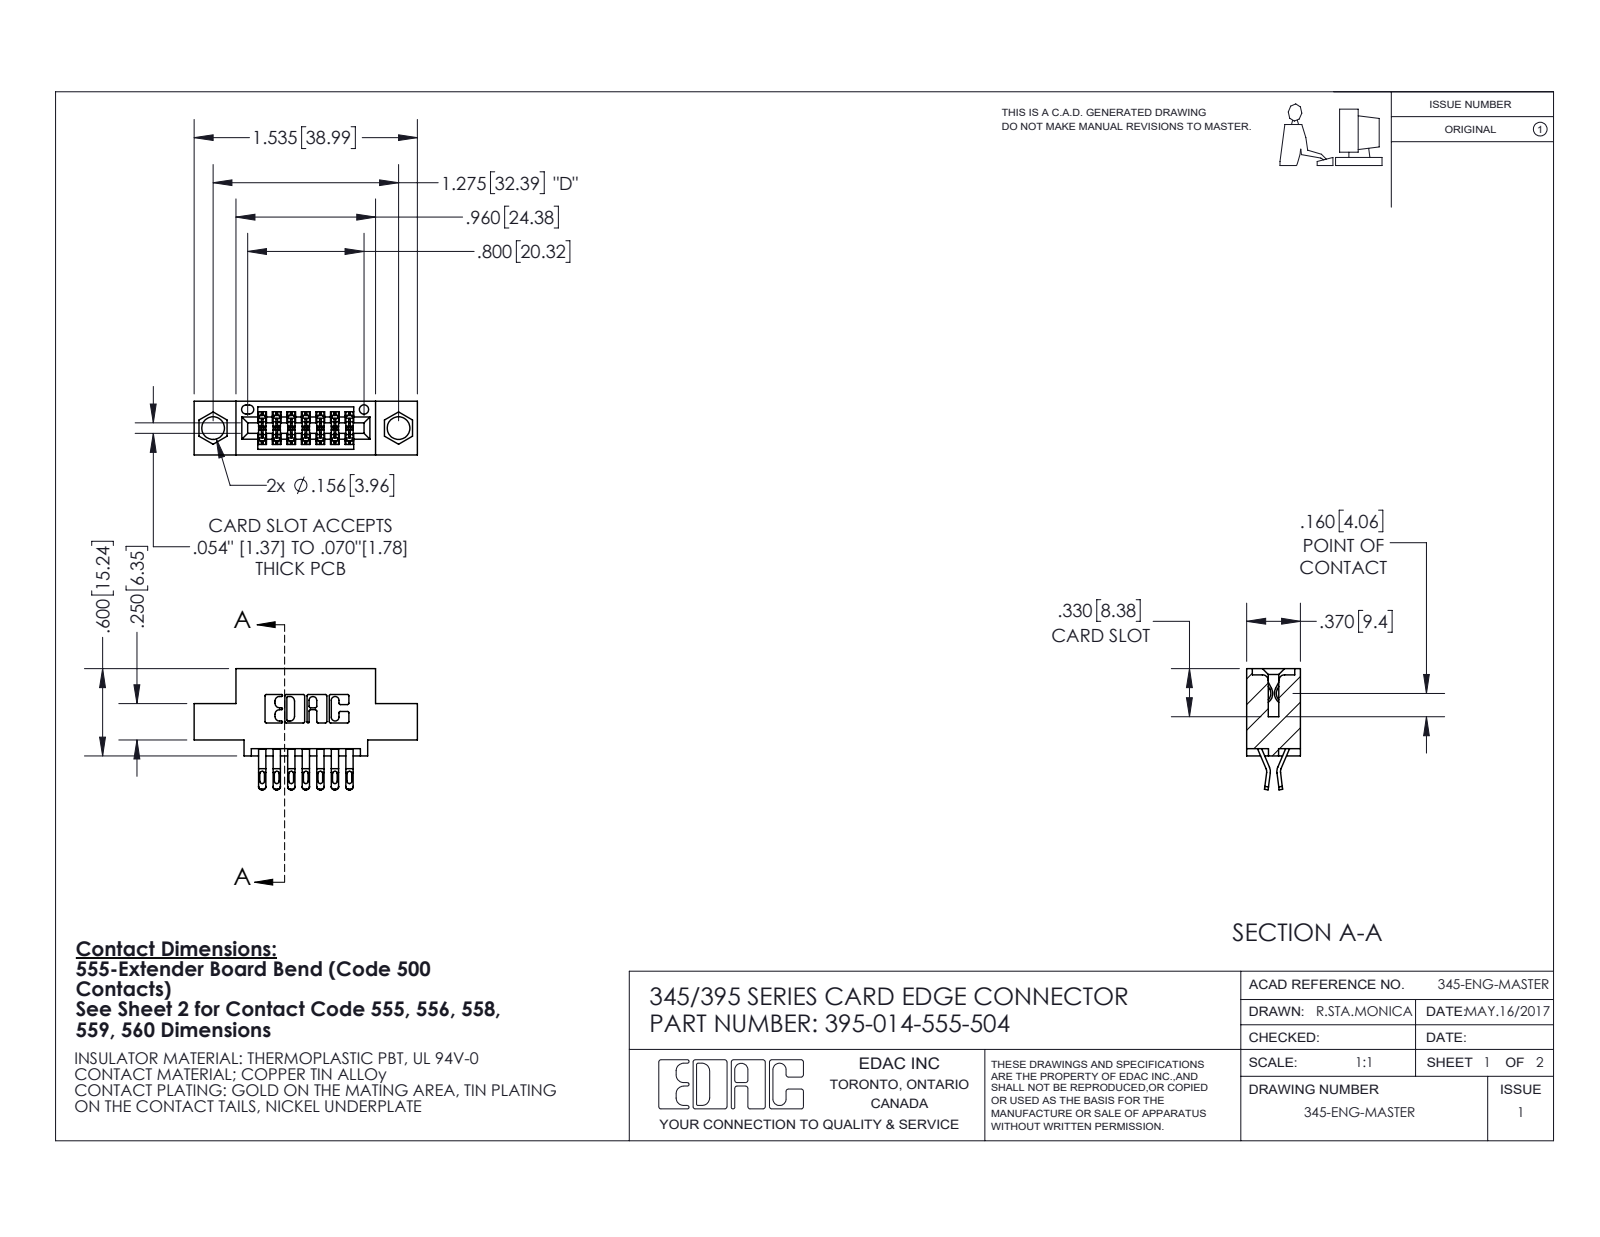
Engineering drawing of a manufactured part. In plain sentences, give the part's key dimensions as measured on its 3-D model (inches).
The part is named "345-292-001_555 Tail; 395-014-555-504; 345 Part_0.110 Offset - 0.156 Dia-TI". Its 3-D file was written by "SolidWorks 2020 (CONFIG_CONTROL_DESIGN)". It is 15 solids with 928 faces: 532 planar, 396 cylindrical and 0 other. Overall it measures 1.535 by 0.832 by 0.37 inches. Its volume is 0.203 cubic inches and its surface area 6.698 square inches. Round holes: 2 of diameter 0.156, 1 of diameter 0.064. Partial cylindrical surfaces (rounded edges, fillets, slot ends): 35 of radius 0.016, 28 of radius 0.006, 28 of radius 0.02, 22 of radius 0.01, 6 of radius 0.007, 6 of radius 0.031, 3 of radius 0.026, 2 of radius 0.01. The main face-to-face distances are 0.2, 0.298, 0.072, 0.37, 0.1, 0.025, 0.3, 0.098, 0.272, 0.16. The hole center spacings are 0.27, 1.045, 1.275.
